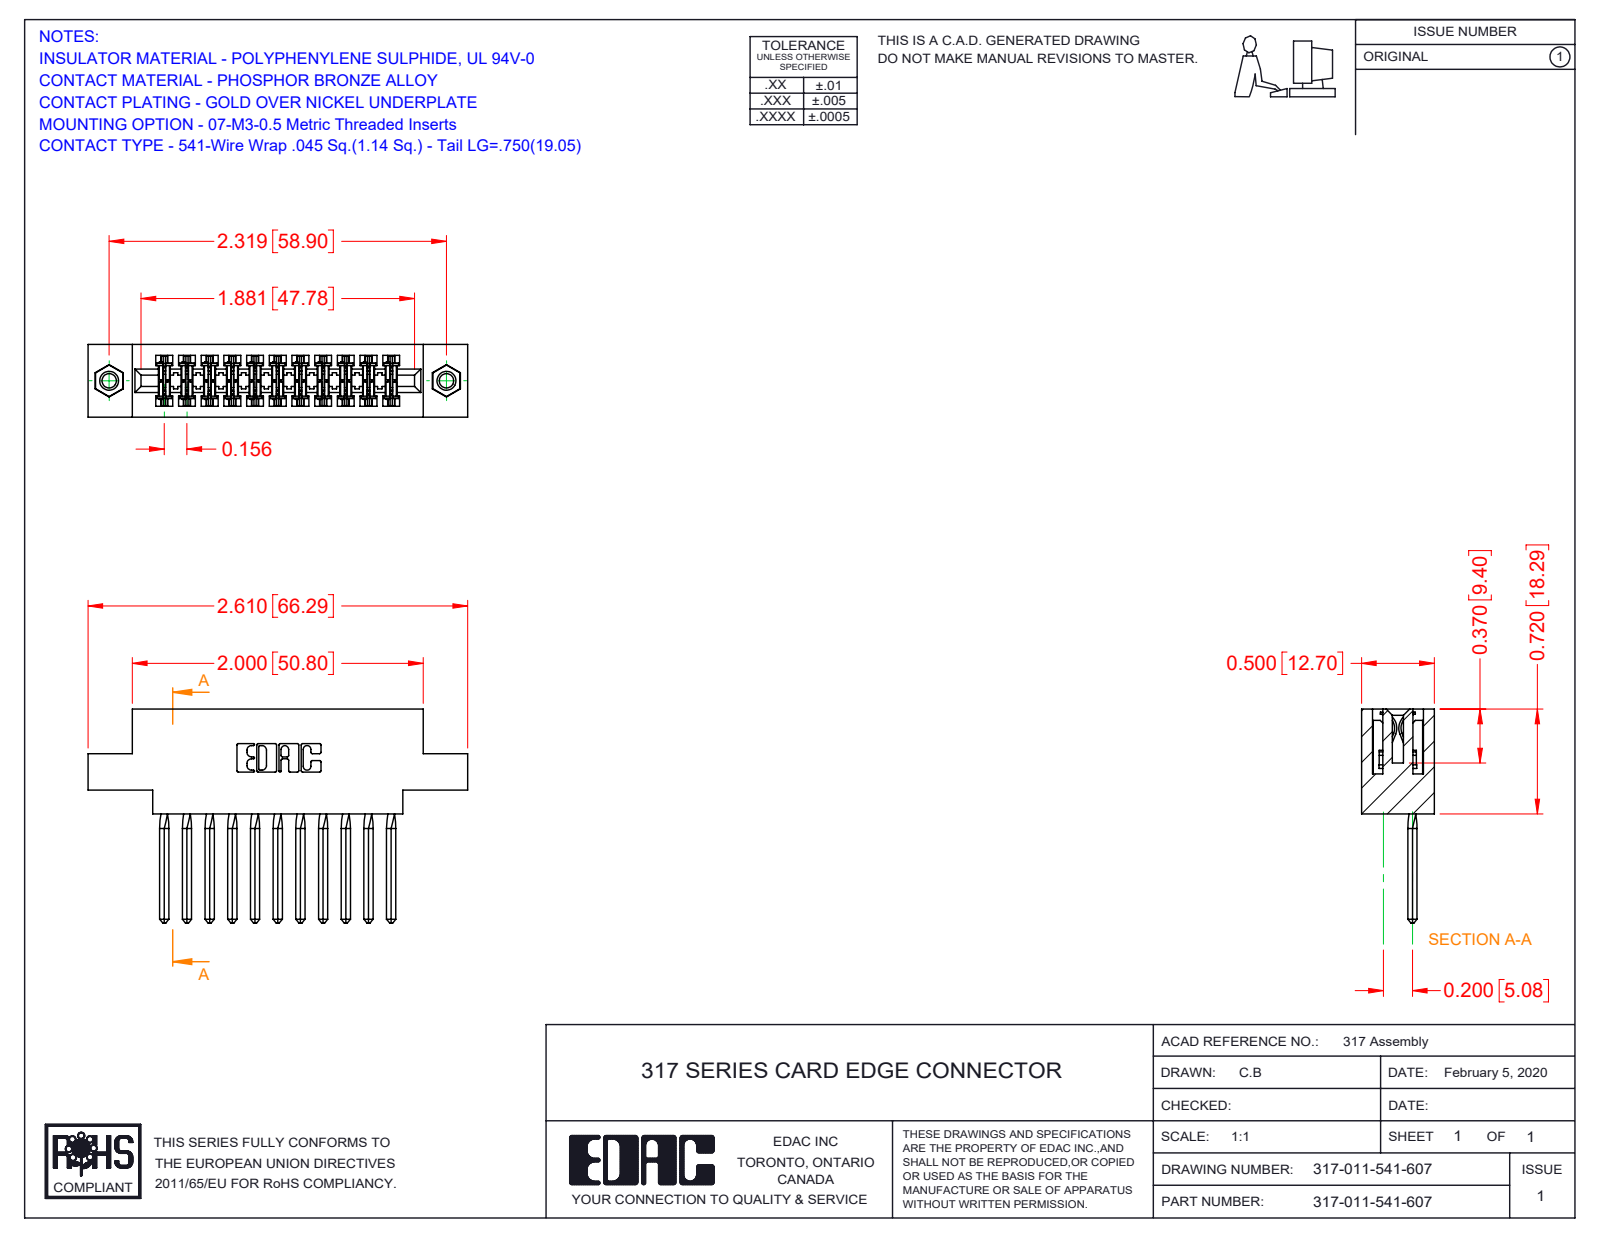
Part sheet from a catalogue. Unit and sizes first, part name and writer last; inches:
Units: inches
Overall size (bounding box): 2.61 × 1.47 × 0.5
Round holes (diameter × count): ⌀0.098 ×2, ⌀0.125 ×2, ⌀0.156 ×2
Round bosses / shafts (diameter × count): ⌀0.155 ×2
Partial cylindrical surfaces — rounded edges, fillets, slot ends (radius × count): R0.01 ×22, R0.015 ×22, R0.007 ×6, R0.031 ×6, R0.026 ×3, R0.095 ×2, R0.1 ×2, R0.11 ×2
Main face-to-face distances: 0.5, 0.075, 0.425, 0.11, 0.22, 0.065, 0.35, 0.331, 0.156, 0.176
Hole centre spacings: 2.319
Volume: 0.597 in³ · Surface area: 19.88 in²
Bodies: 14 solids, 1834 faces (1454 planar, 320 cylindrical, 60 other)
Part name (STEP PRODUCT): 317-290-002_541; 345-250-001_345-250-005-103; 317-011-541-607; 317 Part_.156 Dia - TI
STEP written by: SolidWorks 2016 (CONFIG_CONTROL_DESIGN)
